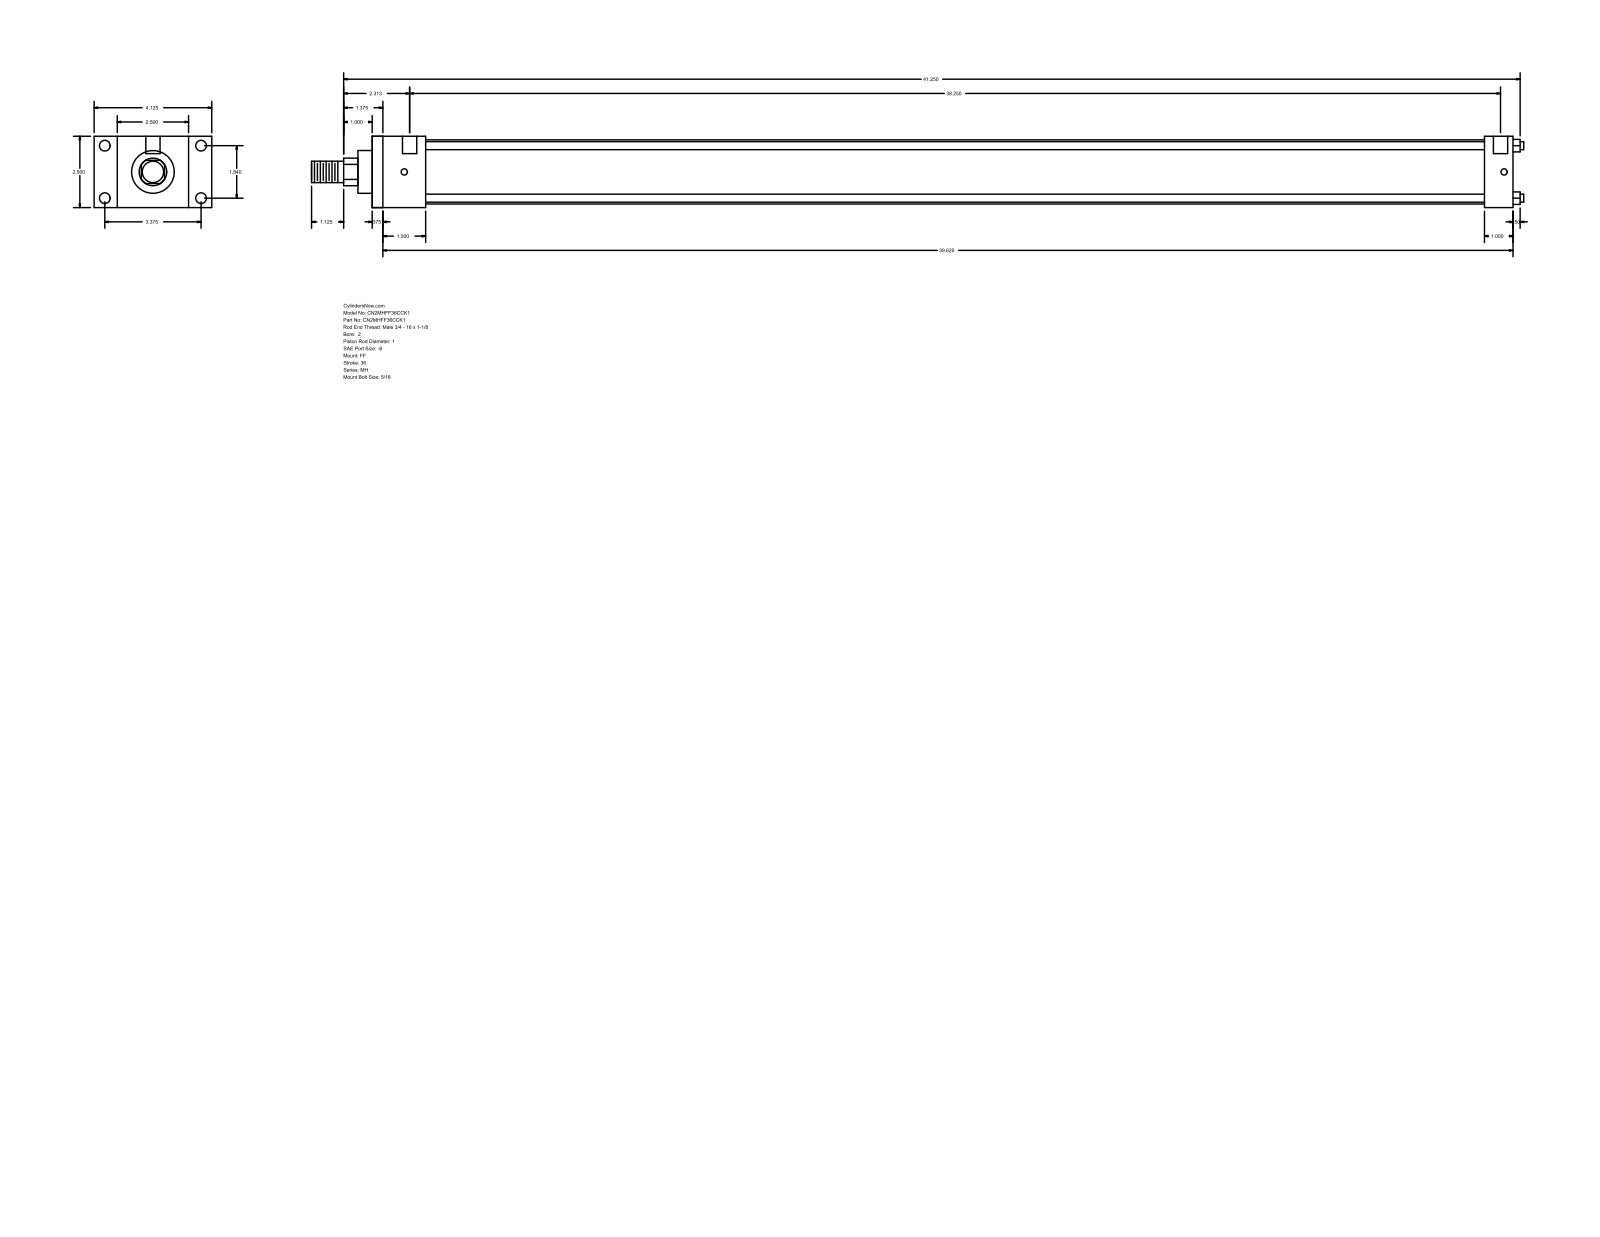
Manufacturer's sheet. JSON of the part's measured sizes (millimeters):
{"part_name": "MH_FF__0200_1", "step_written_by": "GSSL Pune (CONFIG_CONTROL_DESIGN)", "units": "millimeters", "bodies": {"solids": 0, "faces": 92, "planar": 64, "cylindrical": 28, "other": 0}, "overall_size": [1079.5, 104.78, 63.5], "round_holes": [[5.56, 4], [9.53, 4], [12.7, 2]], "round_bosses_or_shafts": [[7.14, 4], [57.15, 1], [38.1, 1], [25.4, 1], [19.05, 1]], "partial_cylinders_radius": [[12.29, 1]], "face_to_face_distances": [63.5, 1016, 9.52, 1006.48, 20.64, 25.4, 47.63, 990.6, 38.11, 981.08], "hole_center_spacings": [46.74, 85.72, 97.63, 979.48, 3.17, 4.76, 971.55, 974.72]}
